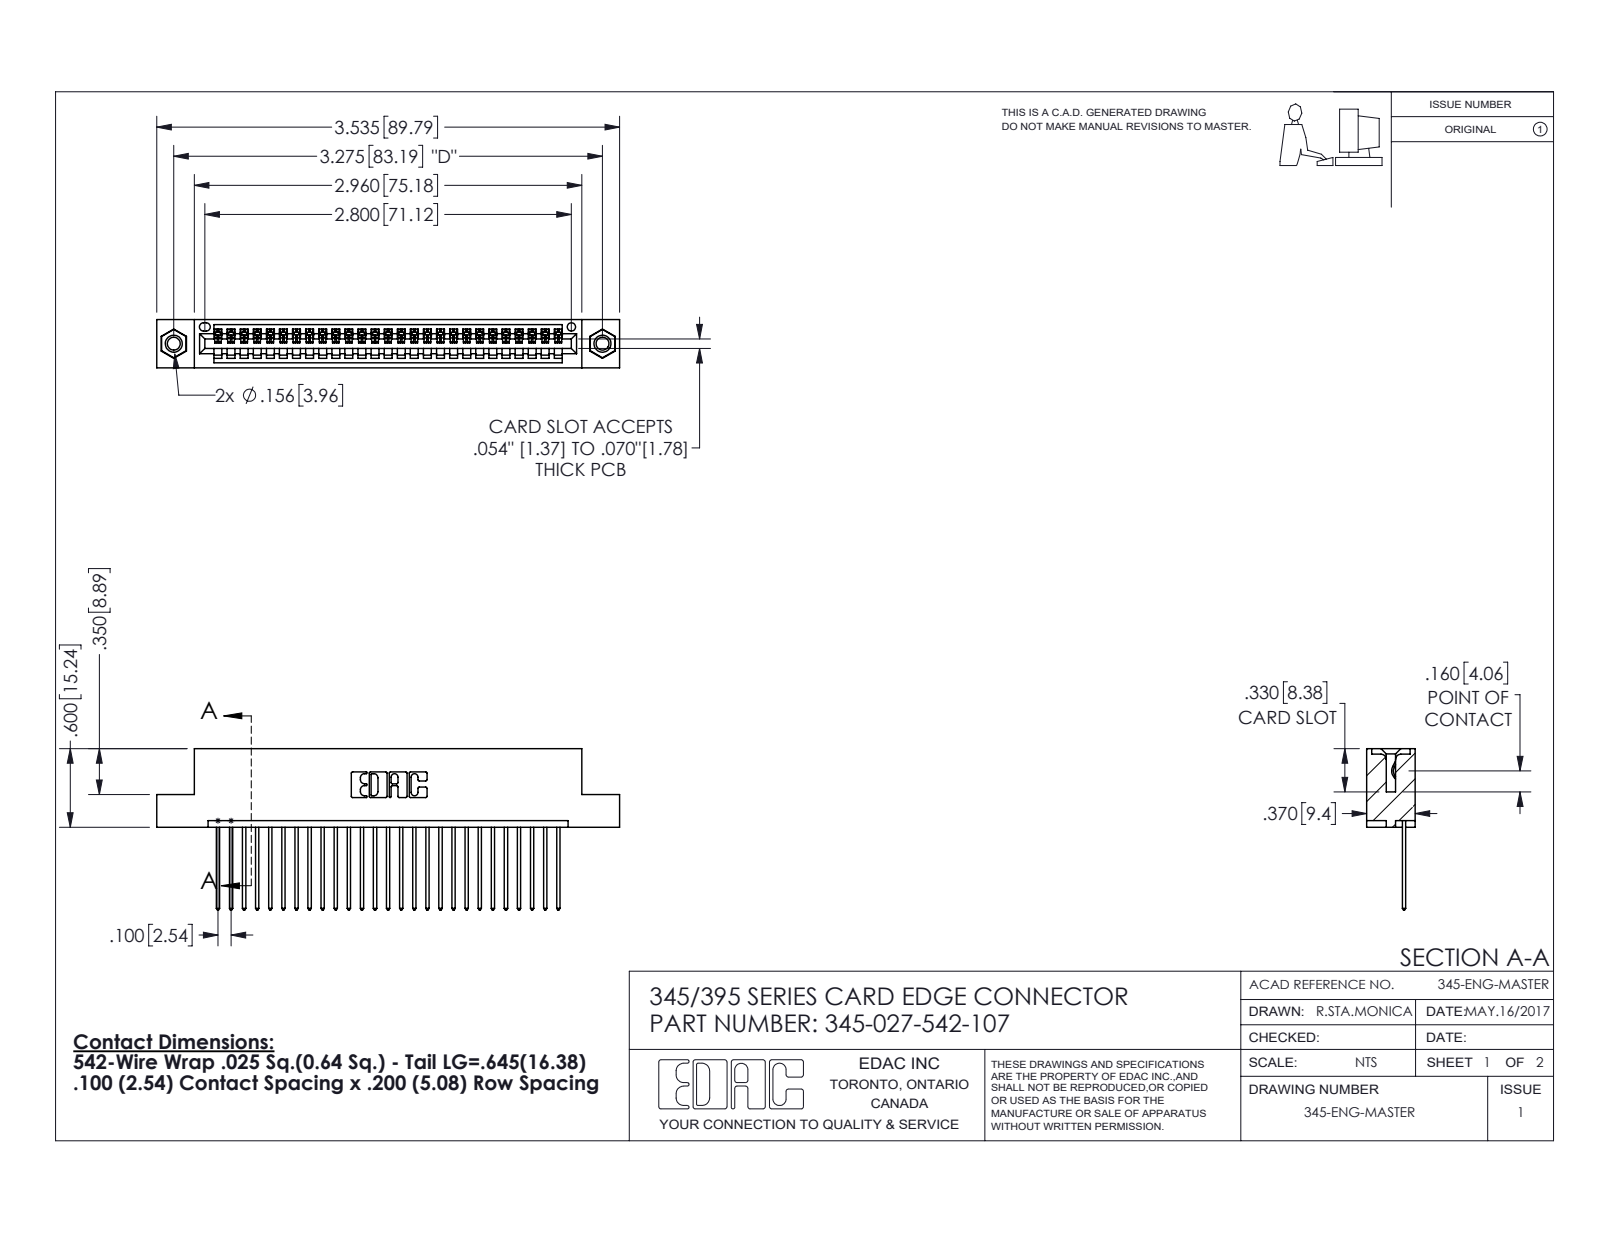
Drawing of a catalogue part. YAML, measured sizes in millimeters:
part_name: "345-250-001_345-250-005-103; 345 Part_Flush Mounting Lugs - 0.156 Dia-TI; 345-027-542-107; 345-292-001_345-293-142"
step_written_by: "SolidWorks 2016 (CONFIG_CONTROL_DESIGN)"
units: millimeters
bodies: {solids: 30, faces: 1752, planar: 1192, cylindrical: 544, other: 16}
overall_size: [89.8, 31.3, 9.4]
volume: 8460
surface_area: 11440
round_holes:
  - {diameter: 2.5, count: 2}
  - {diameter: 3.2, count: 2}
  - {diameter: 4, count: 2}
  - {diameter: 1.6, count: 1}
round_bosses_or_shafts:
  - {diameter: 3.9, count: 2}
partial_cylinders:
  - {radius: 0.2, count: 54}
  - {radius: 0.3, count: 54}
  - {radius: 0.3, count: 22}
  - {radius: 0.2, count: 6}
  - {radius: 0.8, count: 6}
  - {radius: 0.7, count: 3}
  - {radius: 0.8, count: 2}
  - {radius: 1, count: 2}
face_to_face_distances: [1.8, 7.6, 5.1, 9.4, 2.5, 6.9, 0.6, 5.7, 3.8, 1.8]
hole_center_spacings: [6.9, 77.2, 83.2]
